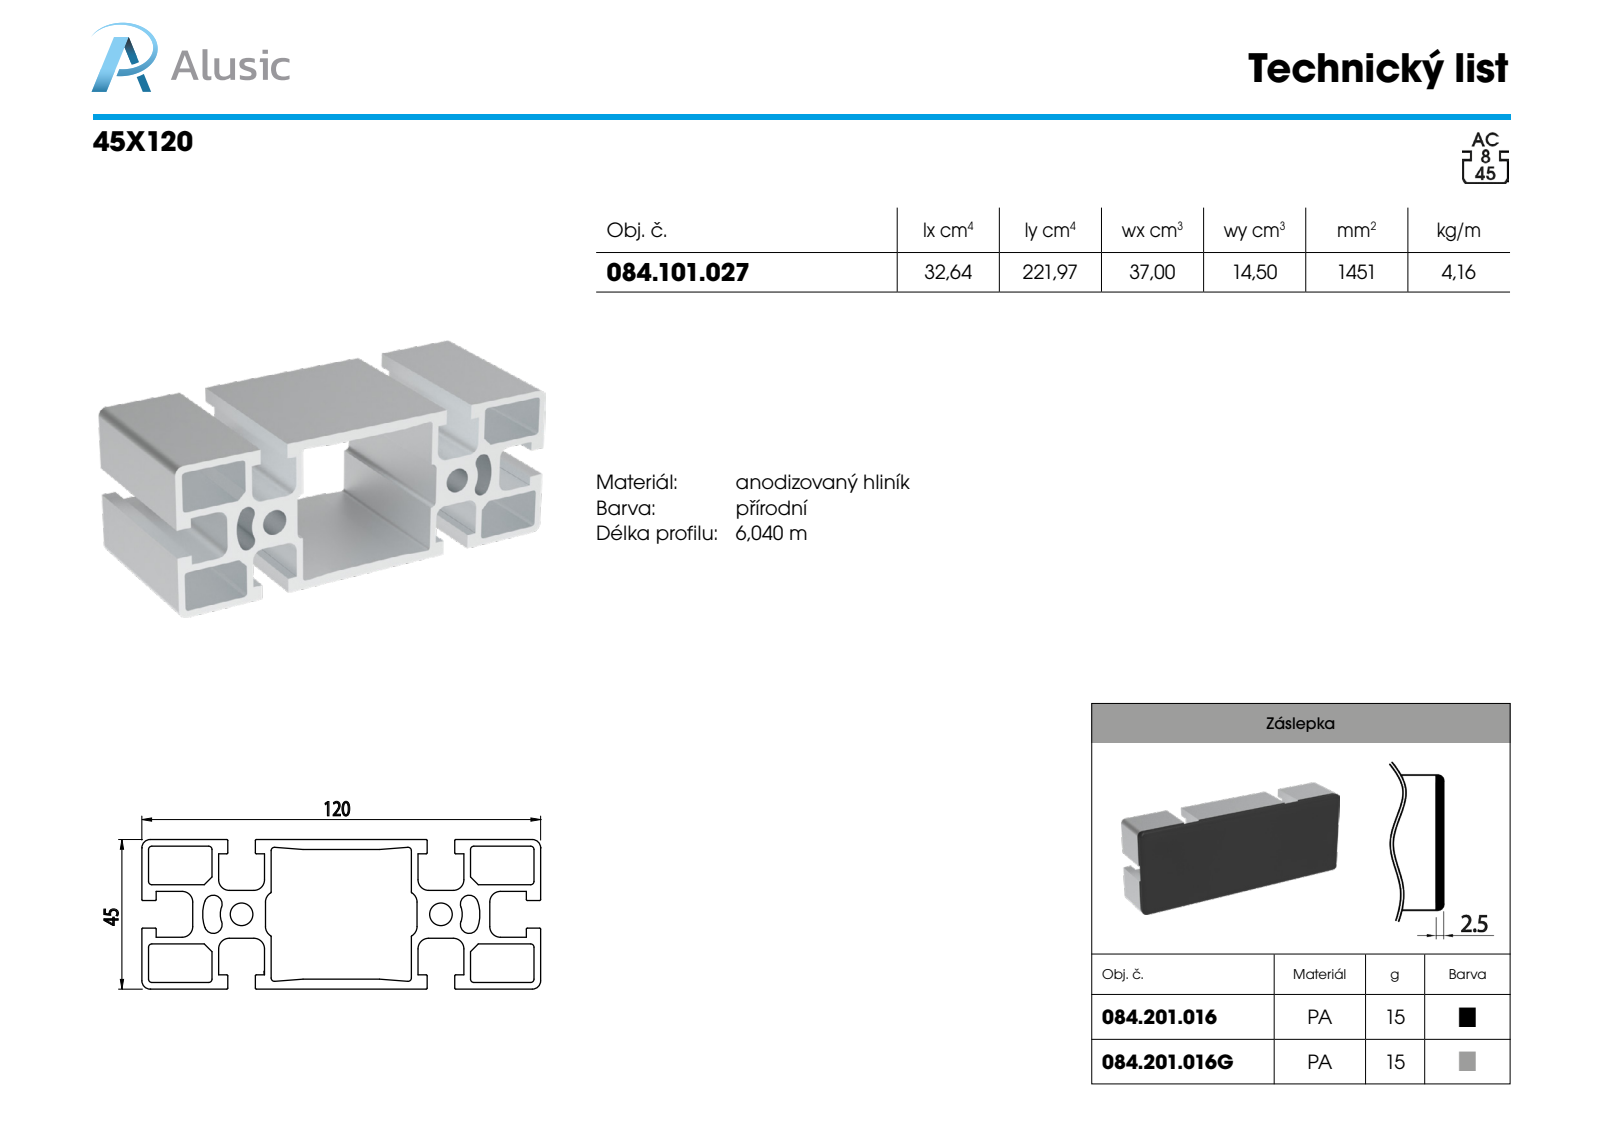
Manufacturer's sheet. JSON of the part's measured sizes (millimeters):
{"part_name": "084.101.027", "step_written_by": "SolidWorks 2018 (AUTOMOTIVE_DESIGN)", "units": "millimeters", "bodies": {"solids": 1, "faces": 142, "planar": 90, "cylindrical": 52, "other": 0}, "overall_size": [120, 100, 45], "volume_mm3": 151943, "surface_area_mm2": 110197, "round_holes": [[7.3, 2]], "partial_cylinders_radius": [[1, 16], [3, 12], [1.6, 4], [2.38, 4], [2.5, 4], [7.1, 2], [11.85, 2]], "face_to_face_distances": [2, 45, 15.8, 13.6, 29.4, 60, 81.1, 36.9, 43, 96.9], "hole_center_spacings": [60]}
